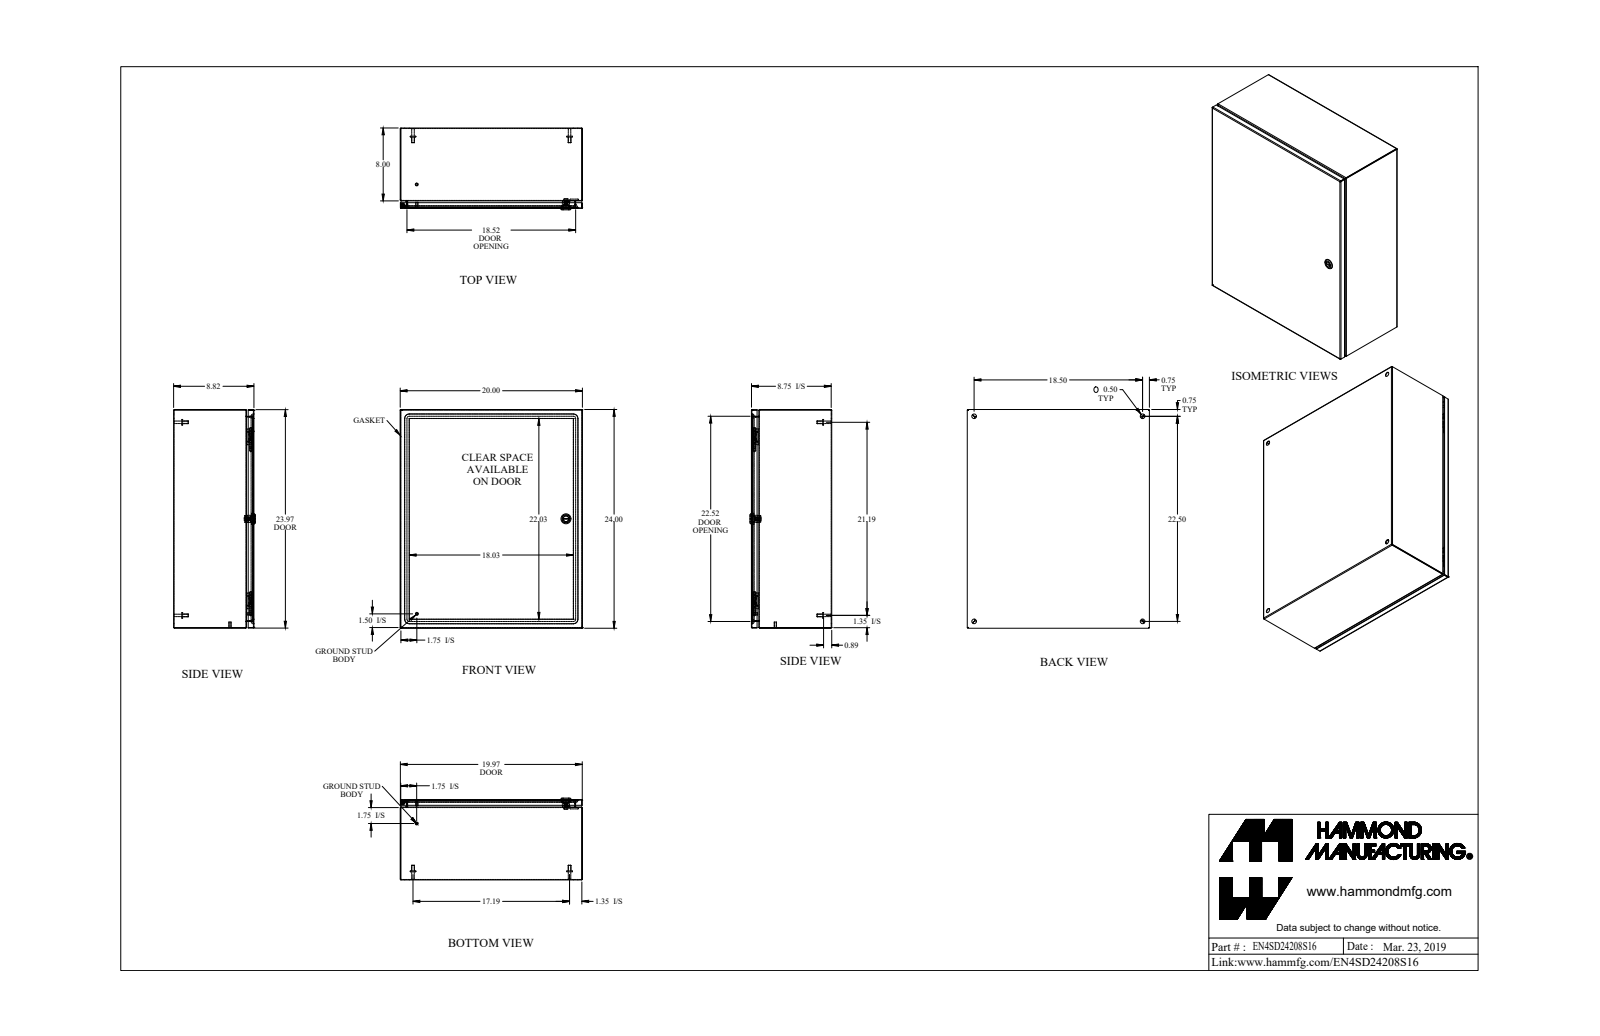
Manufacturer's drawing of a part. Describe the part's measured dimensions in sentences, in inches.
The part is named "EN4SD24208S16_Default". Its 3-D file was written by "SolidWorks 2019 (CONFIG_CONTROL_DESIGN)". It is 22 solids with 656 faces: 303 planar, 211 cylindrical and 142 other. Overall it measures 24 by 20 by 8.981 inches. Its volume is 113.2 cubic inches and its surface area 3 868 square inches. Round holes: 5 of diameter 0.5, 1 of diameter 0.172, 1 of diameter 0.197, 1 of diameter 0.24, 1 of diameter 0.242, 1 of diameter 0.387, 1 of diameter 0.63, 1 of diameter 0.768. Round bosses or shafts: 6 of diameter 0.313, 5 of diameter 0.625, 4 of diameter 0.275, 2 of diameter 0.25, 1 of diameter 1.1, 1 of diameter 0.785, 1 of diameter 0.525, 1 of diameter 0.475. Partial cylindrical surfaces (rounded edges, fillets, slot ends): 21 of radius 0.029, 21 of radius 0.086, 12 of radius 0.188, 4 of radius 0.006, 4 of radius 0.062, 4 of radius 0.25, 4 of radius 0.499, 2 of radius 0.125. The main face-to-face distances are 0.057, 0.057, 8.707, 8.764, 8.764, 8.821, 19.943, 23.943, 19.886, 20. The hole center spacings are 11.3, 18.5, 20.754, 22.5, 29.129.
